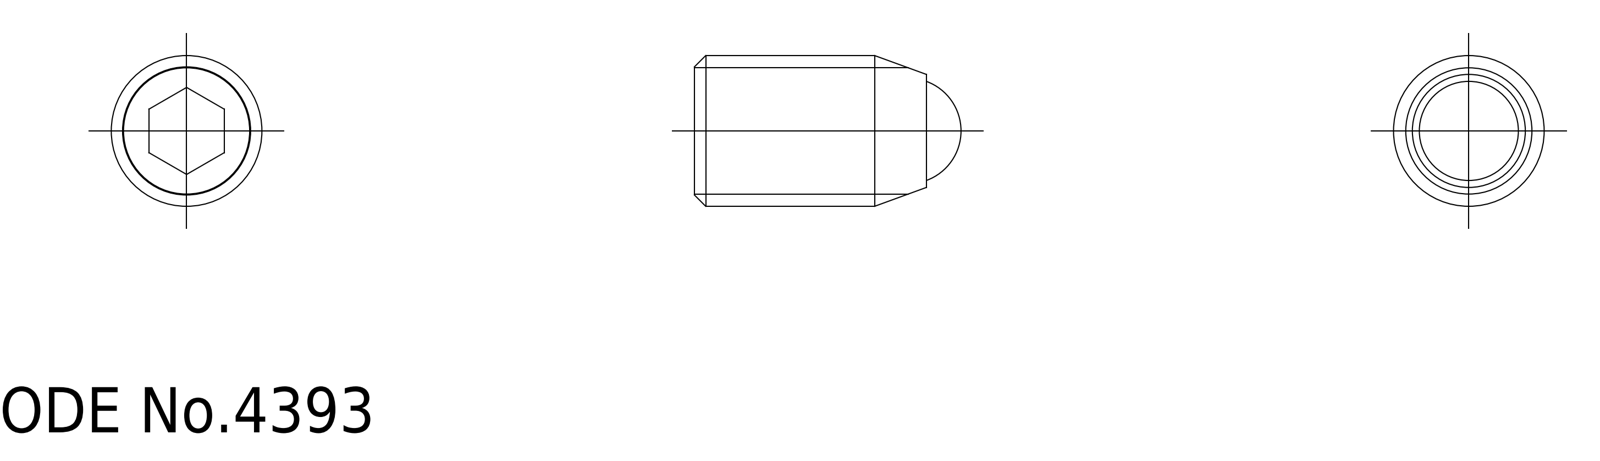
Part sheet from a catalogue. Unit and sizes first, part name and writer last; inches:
Units: inches
Overall size (bounding box): 0.697 × 0.394 × 0.394
Volume: 0.06 in³ · Surface area: 1.5 in²
Bodies: 2 solids, 20 faces (0 planar, 0 cylindrical, 20 other)
Part name (STEP PRODUCT): ball; SCS_M10_16_R_15732_36
STEP written by: CADfix (AUTOMOTIVE_DESIGN)
